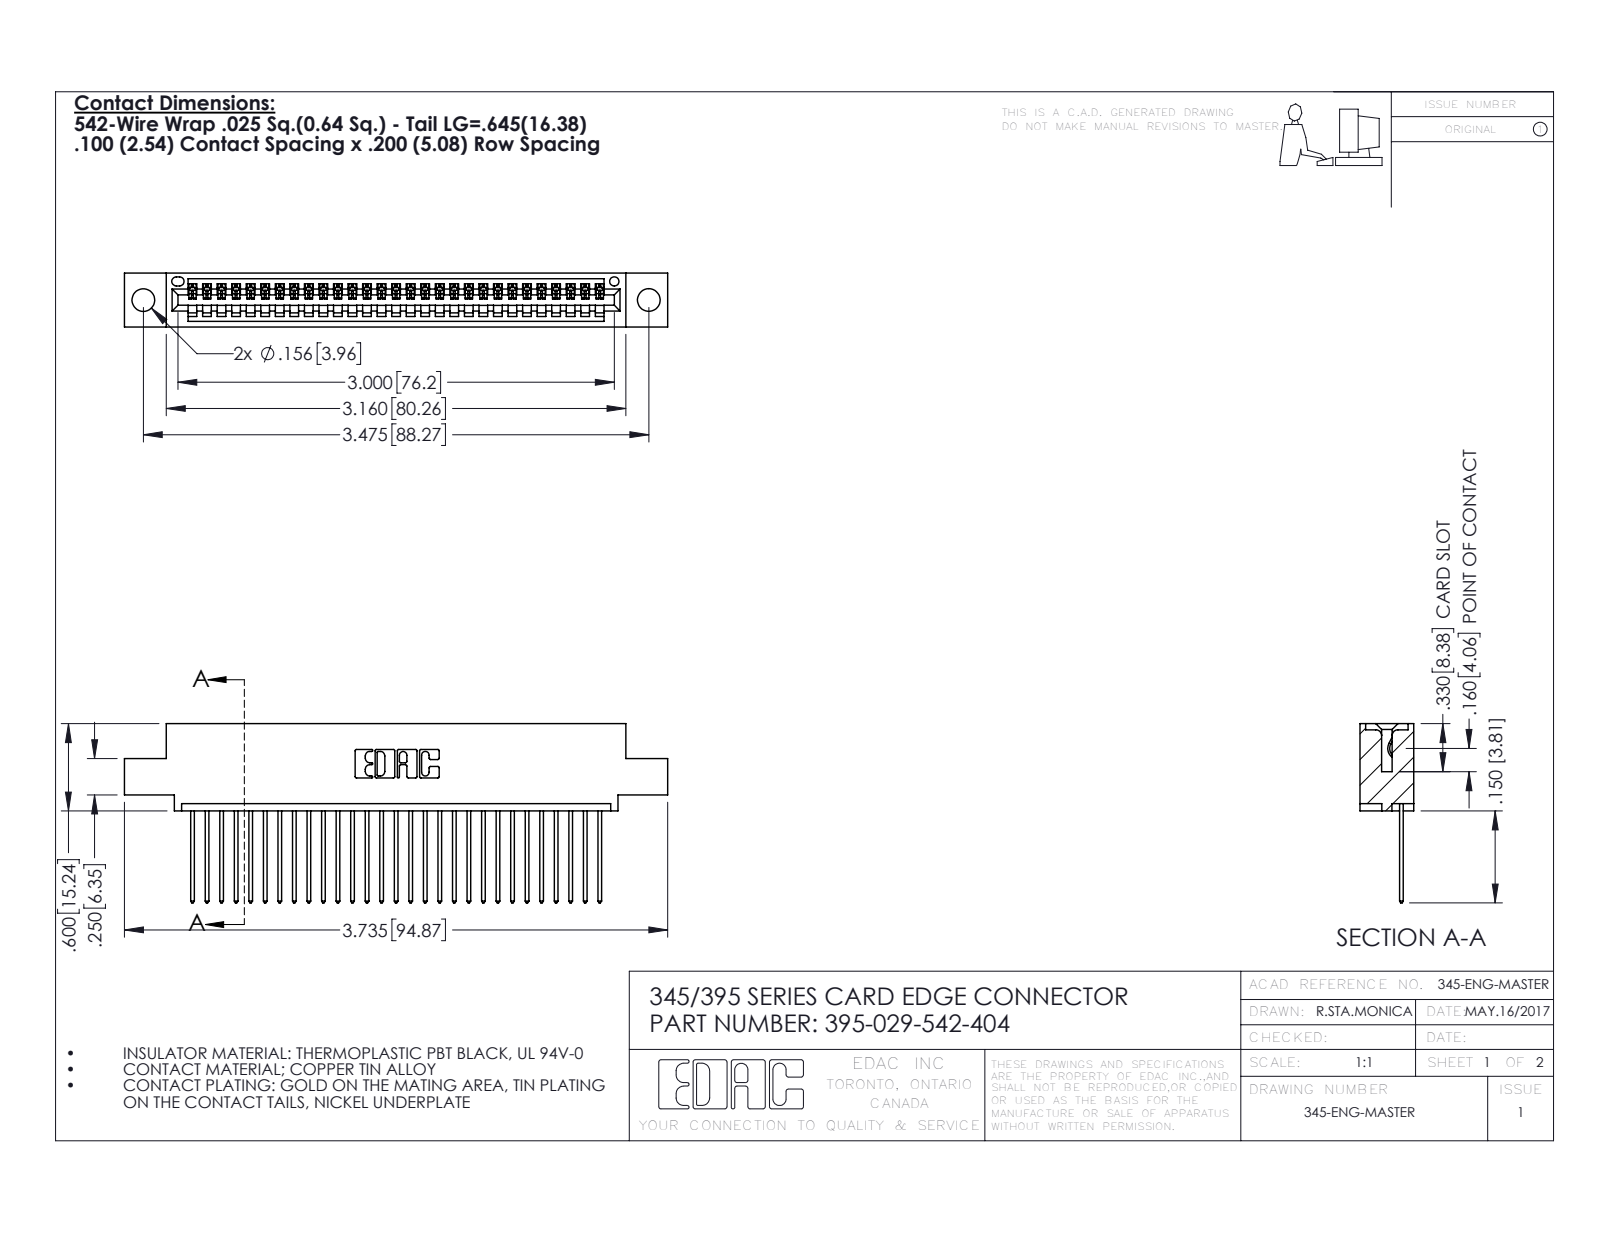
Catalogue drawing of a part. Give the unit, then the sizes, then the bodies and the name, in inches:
Units: inches
Overall size (bounding box): 3.735 × 1.232 × 0.37
Round holes (diameter × count): ⌀0.156 ×2, ⌀0.064 ×1
Partial cylindrical surfaces — rounded edges, fillets, slot ends (radius × count): R0.006 ×58, R0.01 ×58, R0.01 ×22, R0.007 ×6, R0.031 ×6, R0.026 ×3, R0.031 ×2, R0.04 ×2
Main face-to-face distances: 0.298, 0.072, 0.37, 0.098, 0.272, 0.025, 0.2, 0.225, 0.149, 0.072
Hole centre spacings: 0.27, 3.24, 3.475
Volume: 0.537 in³ · Surface area: 18.33 in²
Bodies: 30 solids, 1812 faces (1244 planar, 568 cylindrical, 0 other)
Part name (STEP PRODUCT): 395-029-542-404; 345-292-001_345-293-142; 345 Part_0.110 Offset - 0.156 Dia-TH
STEP written by: SolidWorks 2016 (CONFIG_CONTROL_DESIGN)
